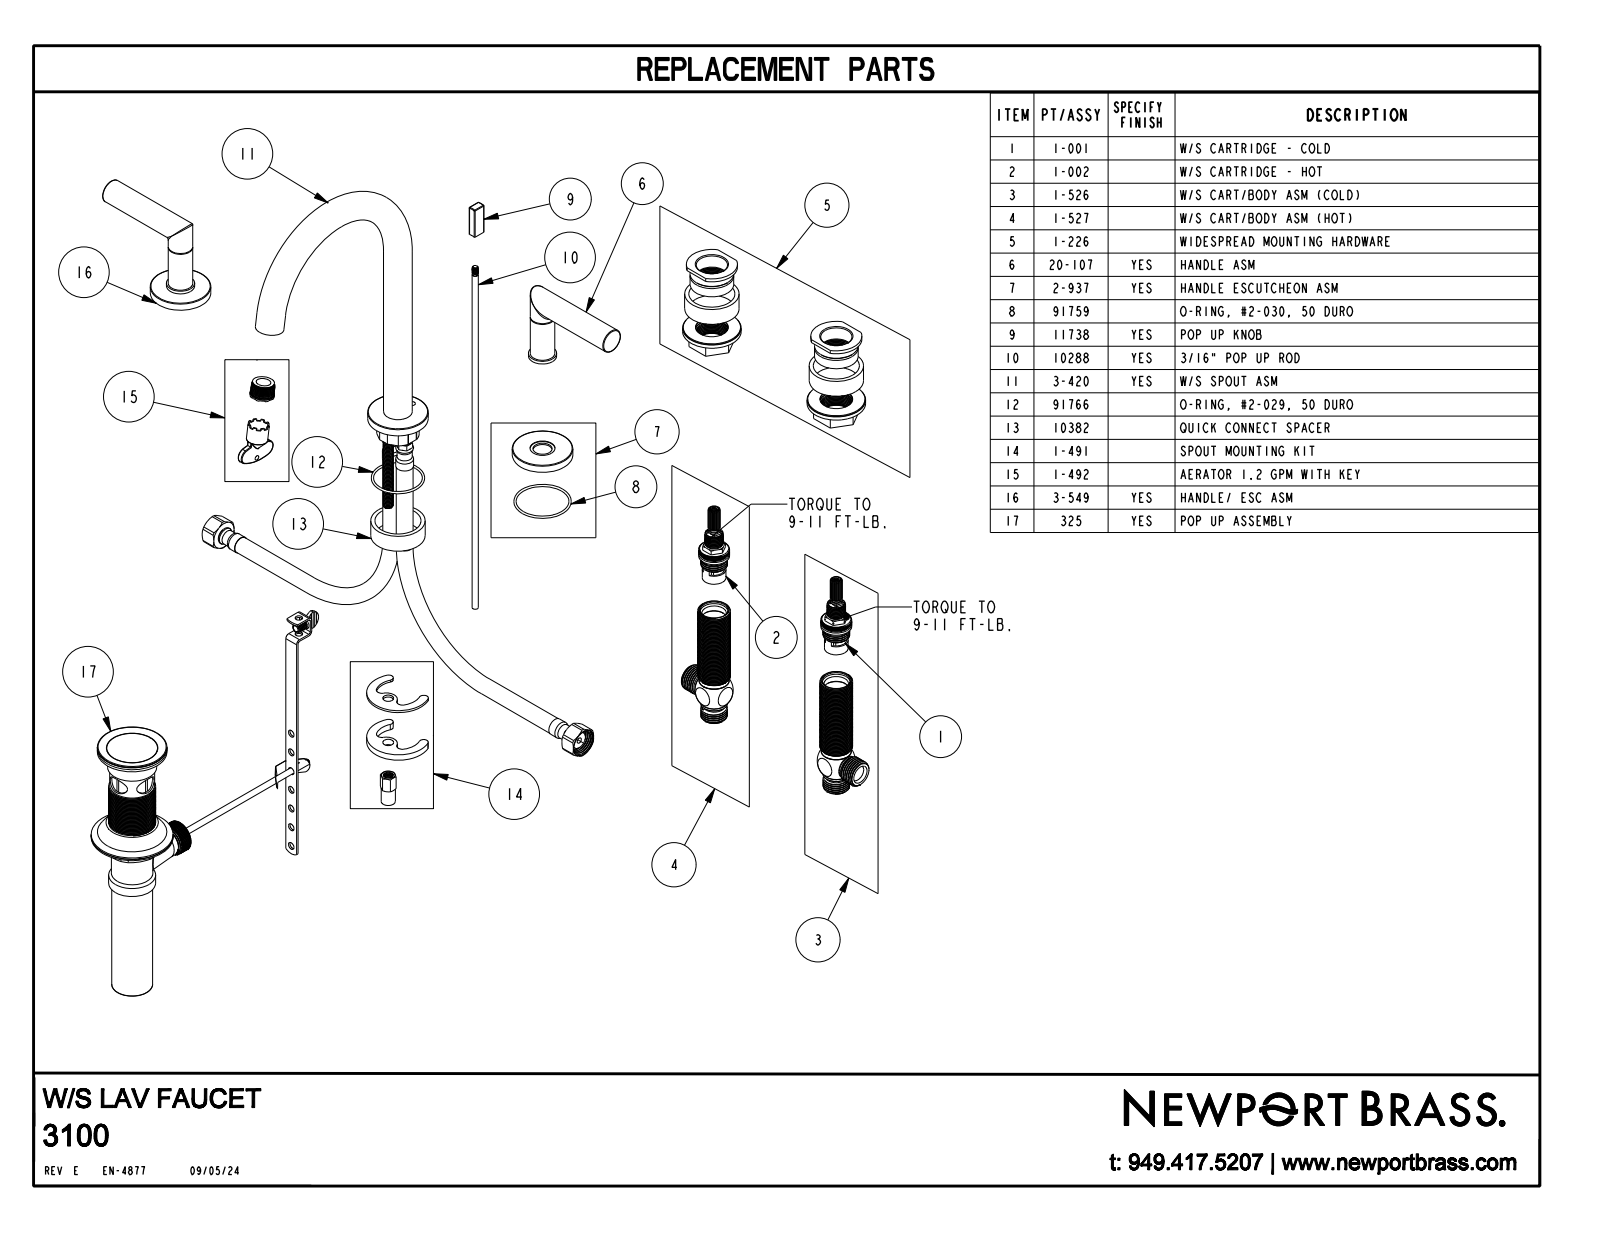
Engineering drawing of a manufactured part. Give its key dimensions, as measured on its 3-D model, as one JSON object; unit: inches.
{"part_name": "3100", "step_written_by": "CREO PARAMETRIC BY PTC INC, 2018400 (CONFIG_CONTROL_DESIGN)", "units": "inches", "bodies": {"solids": 3, "faces": 90, "planar": 20, "cylindrical": 42, "other": 28}, "overall_size": [14, 9.444, 6.901], "volume_in3": 15.47, "surface_area_in2": 87.48, "round_bosses_or_shafts": [[1.85, 3], [0.75, 3], [0.875, 2], [0.86, 2], [0.506, 2]], "partial_cylinders_radius": [[0.02, 6], [0.47, 1], [0.876, 1]], "face_to_face_distances": [0.25, 6.875, 7.125, 1.701, 1.732, 1.451, 1.482, 0.031, 14, 0.25]}
